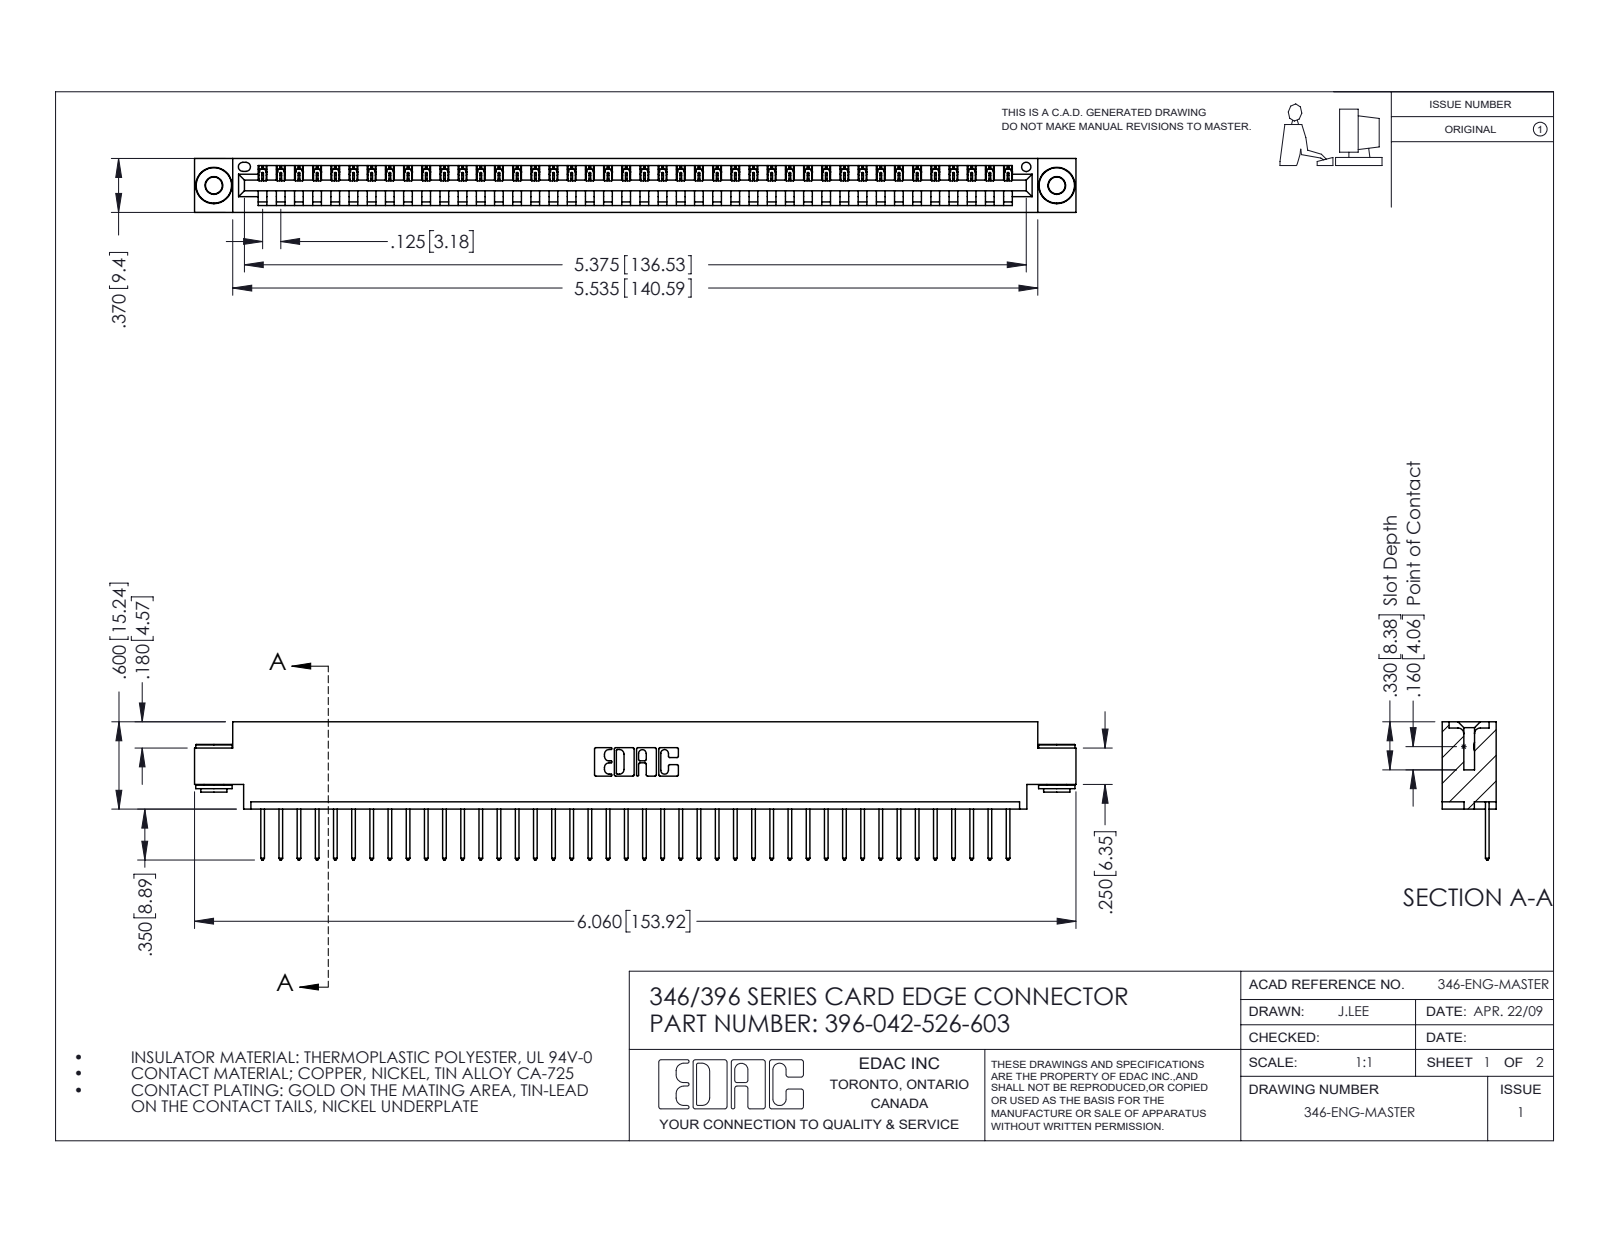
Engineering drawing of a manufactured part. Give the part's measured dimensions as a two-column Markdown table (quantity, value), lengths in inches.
| quantity | value |
| --- | --- |
| part name | 345-250-002_345-250-002-102; 345-292-001_345-293-126; 346 Part_0.170 Offset - 0.156 Dia-TH; 396-042-526-603 |
| STEP written by | SolidWorks 2016 (CONFIG_CONTROL_DESIGN) |
| units | inches |
| bodies | 45 solids, 2600 faces (1770 planar, 822 cylindrical, 8 other) |
| overall size | 6.06 × 0.95 × 0.37 |
| volume | 0.889 in³ |
| surface area | 28.74 in² |
| round holes (diameter × count) | 0.116 × 2, 0.156 × 2, 0.064 × 1 |
| round bosses / shafts (diameter × count) | 0.25 × 2, 0.18 × 2, 0.136 × 2 |
| partial cylindrical surfaces (radius × count) | 0.006 × 84, 0.01 × 84, 0.01 × 22, 0.007 × 6, 0.031 × 6, 0.026 × 3, 0.031 × 2, 0.04 × 2 |
| main face-to-face distances | 0.048, 0.322, 0.37, 0.25, 0.025, 0.072, 0.298, 0.148, 0.222, 0.1 |
| hole center spacings | 0.246, 5.586, 5.795 |
